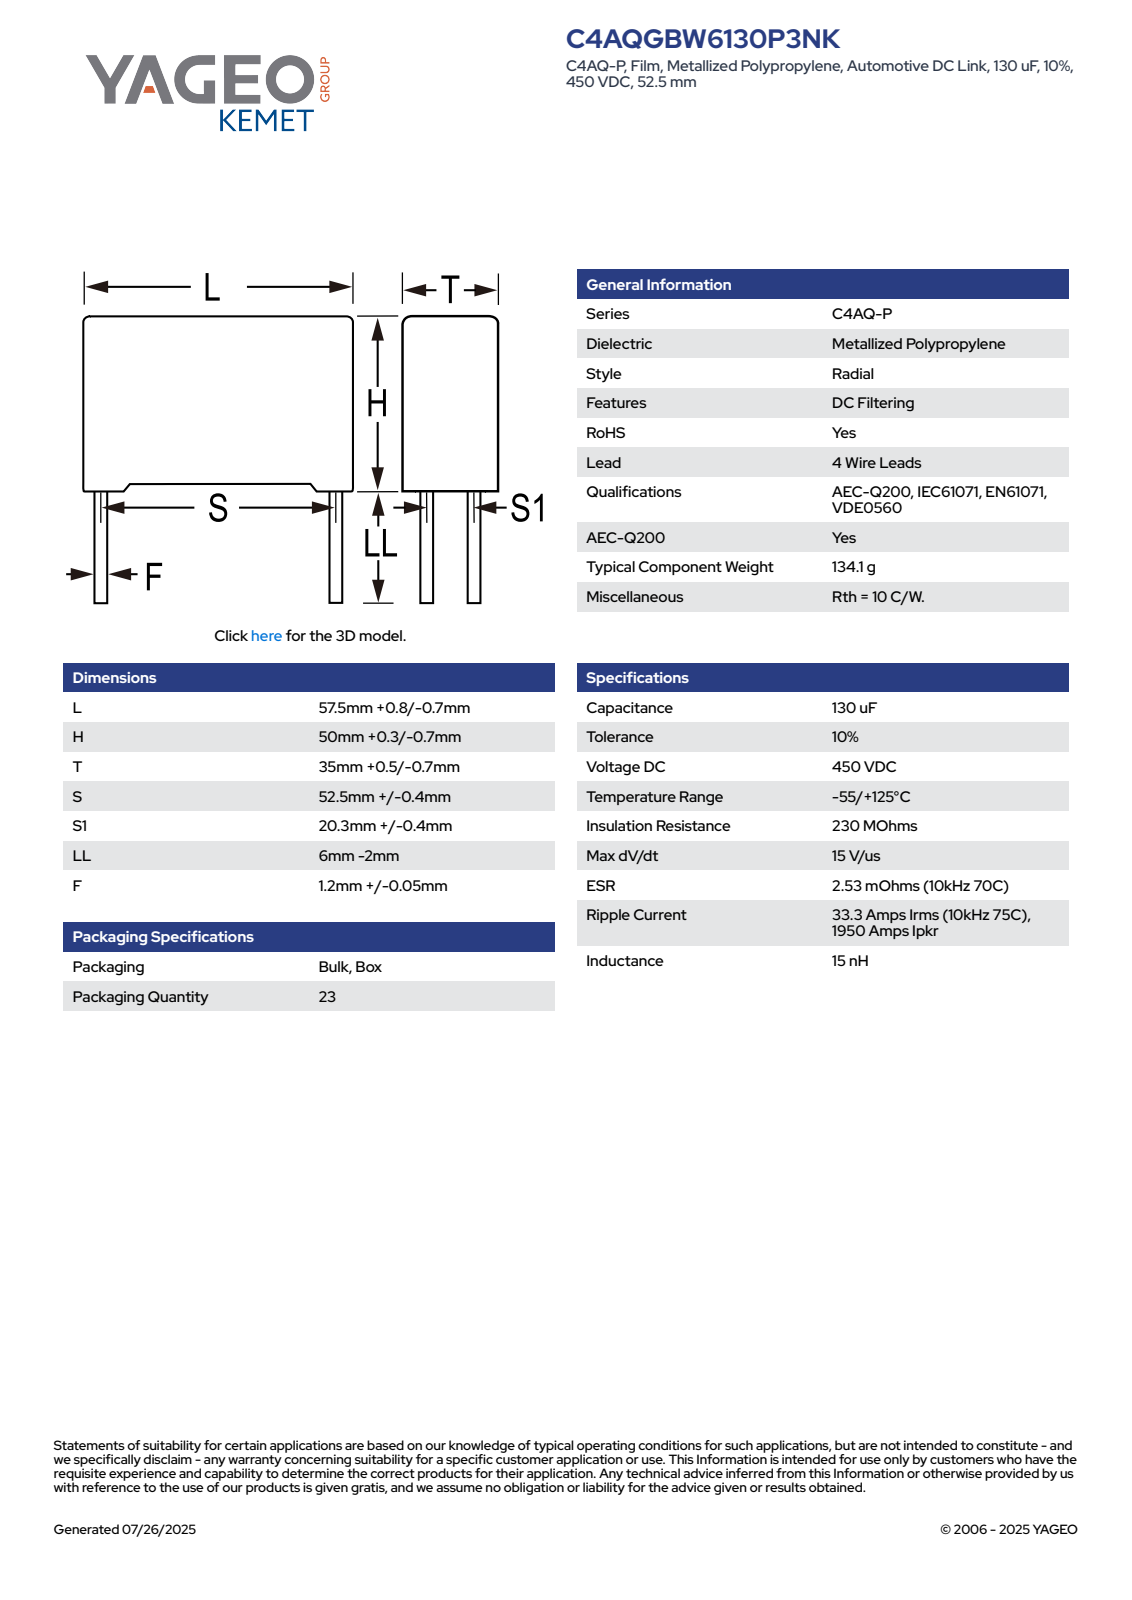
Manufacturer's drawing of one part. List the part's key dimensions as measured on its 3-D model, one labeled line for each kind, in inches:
Part name (STEP PRODUCT): CFP_RB4_57.5X50X35_L58.3H50.3T35.5S52.5S120.3LL4F1.25
STEP written by: SolidWorks 2014 (AUTOMOTIVE_DESIGN)
Units: inches
Bodies: 4 solids, 87 faces (79 planar, 8 cylindrical, 0 other)
Overall size (bounding box): 2.295 × 2.138 × 1.398
Volume: 6.186 in³ · Surface area: 21.52 in²
Round bosses / shafts (diameter × count): ⌀0.049 ×4
Main face-to-face distances: 1.398, 1.922, 2.295, 0.058, 1.98, 0.086, 2.209, 2.124, 1.312, 1.226
